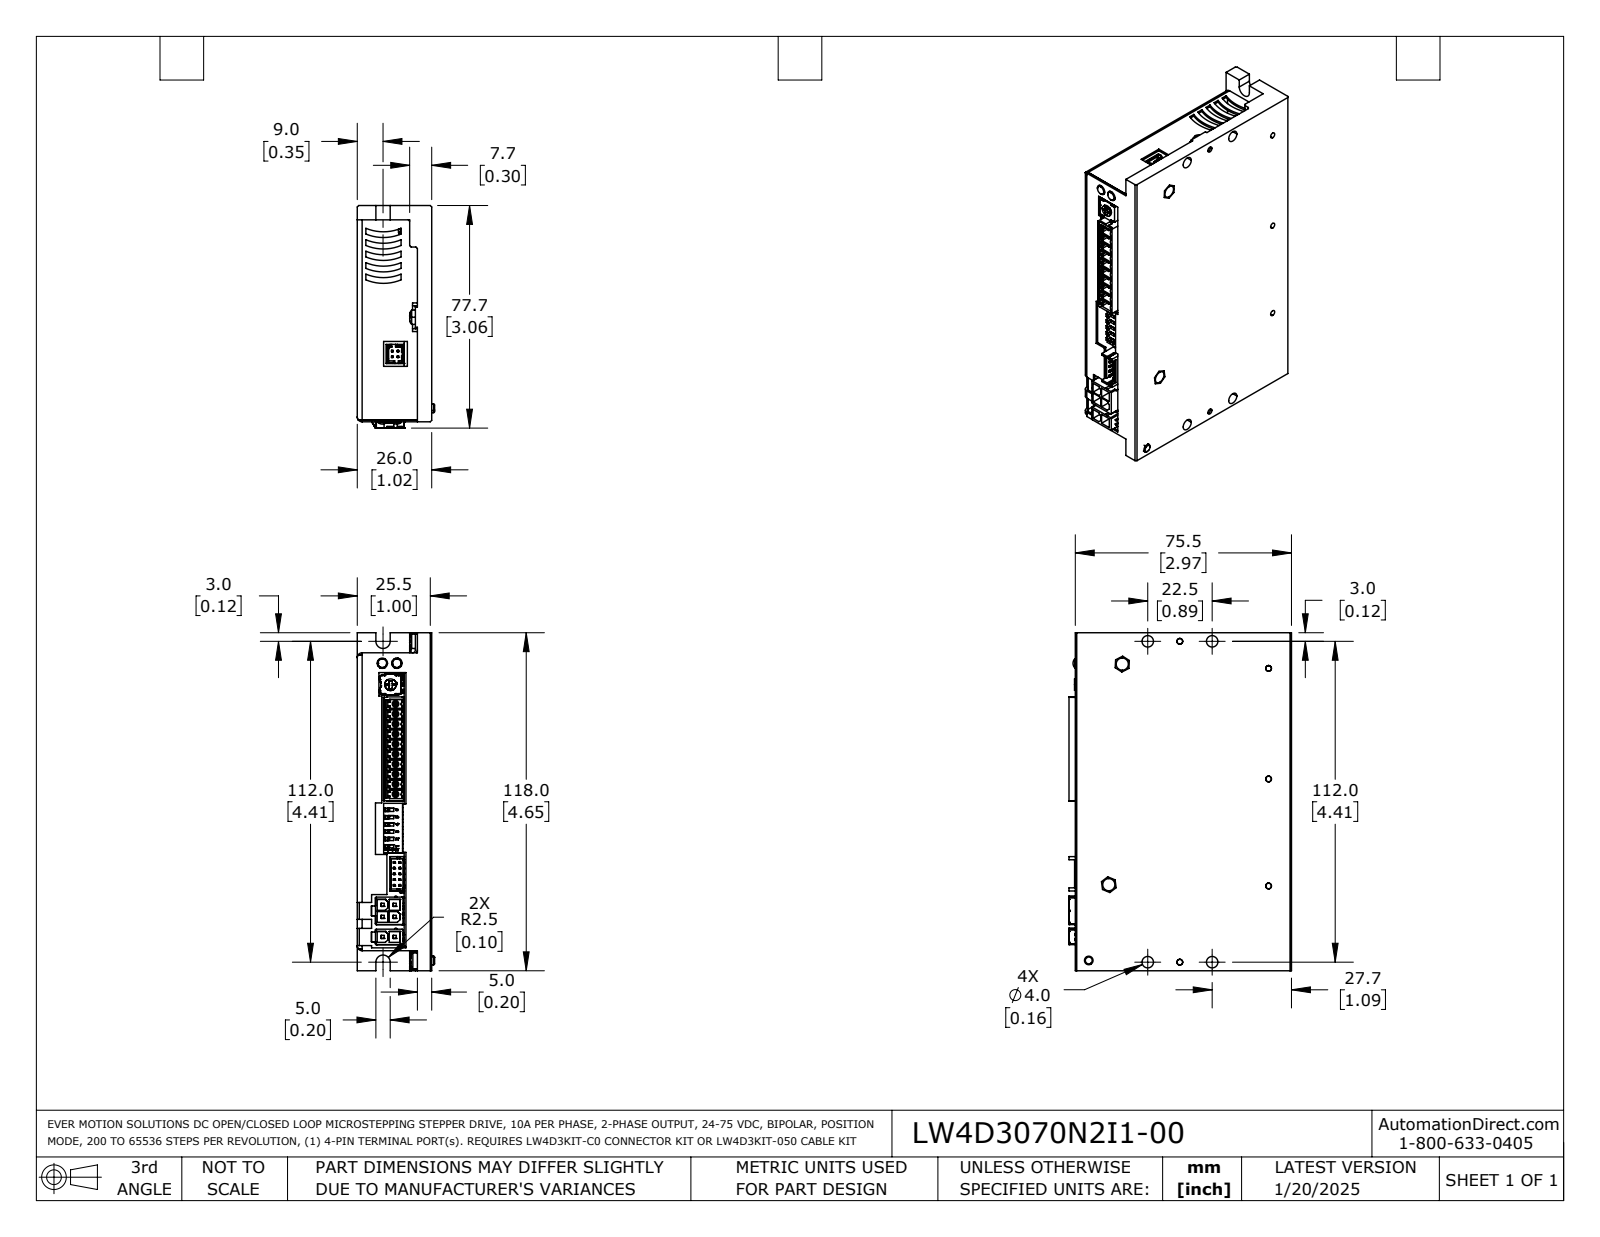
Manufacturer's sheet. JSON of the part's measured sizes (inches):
{"part_name": "LW4D3070N2I1-00", "step_written_by": "SolidWorks 2021 (AUTOMOTIVE_DESIGN)", "units": "inches", "bodies": {"solids": 22, "faces": 3302, "planar": 2271, "cylindrical": 813, "other": 218}, "overall_size": [4.646, 3.059, 1.063], "volume_in3": 5.054, "surface_area_in2": 115, "round_holes": [[0.03, 19], [0.035, 14], [0.039, 12], [0.047, 10], [0.049, 10], [0.031, 6], [0.071, 6], [0.106, 5], [0.118, 4], [0.157, 4], [0.079, 3], [0.098, 3]], "round_bosses_or_shafts": [[0.197, 7], [0.098, 4], [0.162, 2], [0.148, 2], [0.12, 2], [0.236, 1], [0.157, 1], [0.118, 1]], "partial_cylinders_radius": [[0.004, 103], [0.015, 28], [0.012, 18], [0.059, 12], [0.02, 11], [0.63, 10], [0.024, 9], [0.004, 6]], "face_to_face_distances": [0.028, 0.197, 0.316, 1.024, 0.708, 0.063, 0.996, 0.68, 0.799, 0.379], "hole_center_spacings": [0.1, 0.138, 0.276, 0.141, 0.224, 0.2, 0.413, 0.551]}
